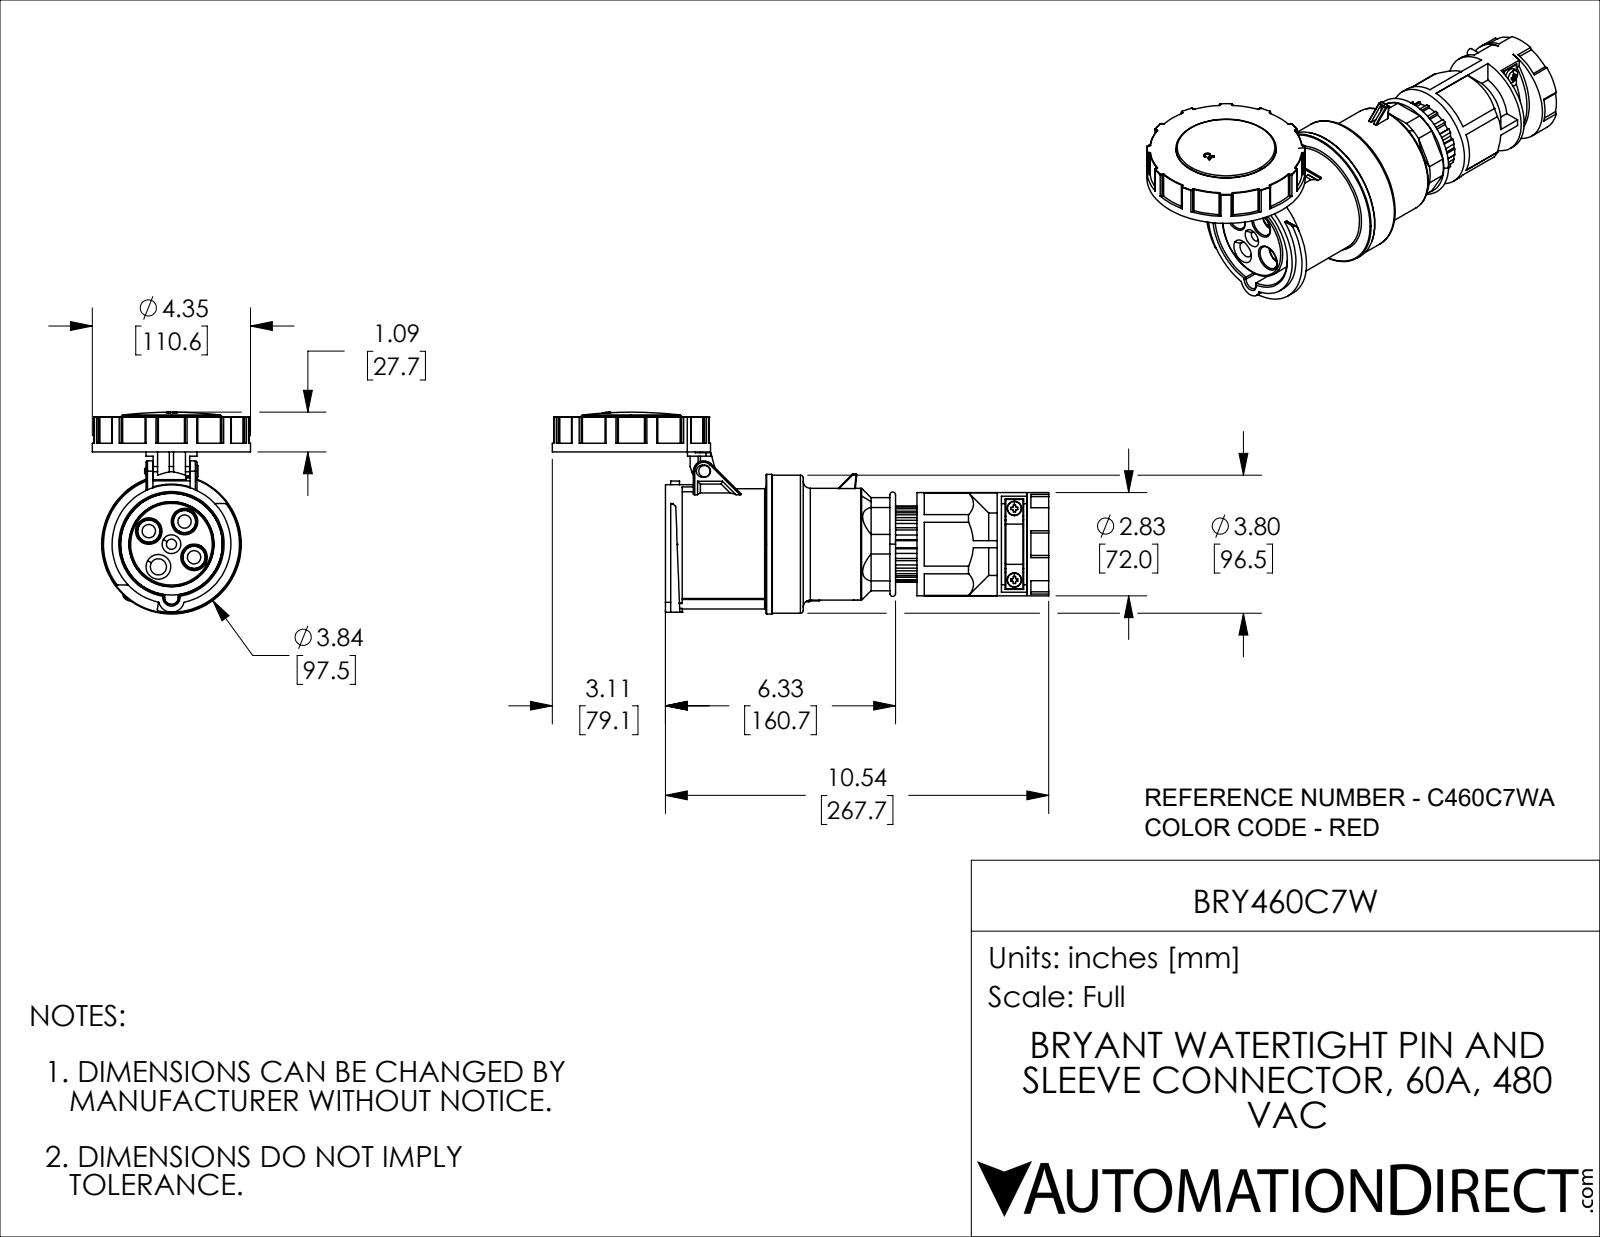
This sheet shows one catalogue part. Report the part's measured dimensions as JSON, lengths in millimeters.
{"part_name": "BRY460C7W", "step_written_by": "SolidWorks 2021 (CONFIG_CONTROL_DESIGN)", "units": "millimeters", "bodies": {"solids": 2, "faces": 1151, "planar": 476, "cylindrical": 393, "other": 282}, "overall_size": [346.77, 140.9, 110.55], "volume_mm3": 1153000, "surface_area_mm2": 181231, "round_holes": [[9.3, 3], [7.1, 1], [11.3, 1], [37, 1], [65.5, 1], [100.6, 1]], "round_bosses_or_shafts": [[5, 3], [110.55, 1], [97.5, 1], [96.5, 1], [83, 1], [78, 1], [77.6, 1], [72, 1]], "partial_cylinders_radius": [[0.3, 48], [1, 40], [0.5, 15], [34.5, 6], [0.4, 4], [2, 4], [1.75, 2], [2.5, 2]], "face_to_face_distances": [21.5, 3, 65, 26, 15.5, 92, 15, 161.5, 5, 164.5], "hole_center_spacings": [18.24, 25.8, 36.49]}
